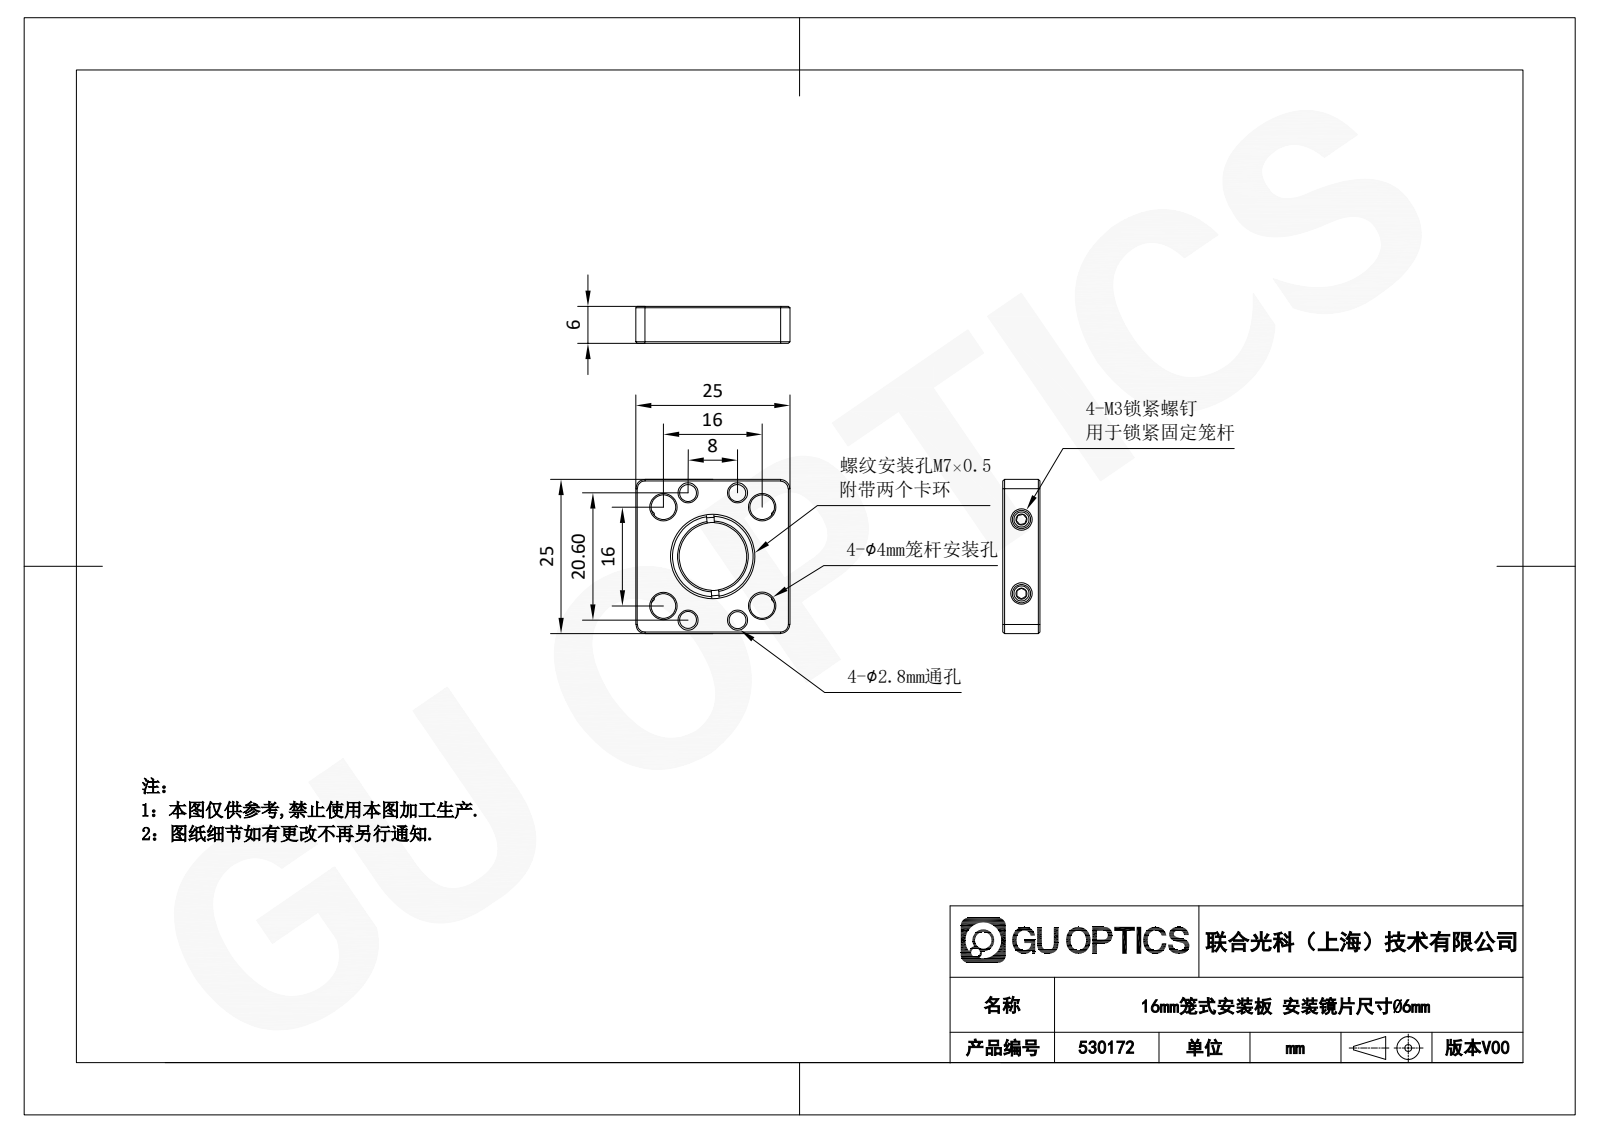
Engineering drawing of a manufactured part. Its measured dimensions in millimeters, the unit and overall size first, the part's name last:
Units: millimetres
Overall size (bounding box): 25 × 25 × 6
Round holes (diameter × count): ⌀2.8 ×4, ⌀4 ×4, ⌀2.5 ×2, ⌀4.5 ×1, ⌀6.5 ×1
Round bosses / shafts (diameter × count): ⌀3 ×2, ⌀7 ×1
Partial cylindrical surfaces — rounded edges, fillets, slot ends (radius × count): R1.5 ×4
Main face-to-face distances: 6, 25, 2, 21.56, 4, 3, 22, 1.5, 1, 24
Hole centre spacings: 4.61, 11.05, 11.31, 12.22, 16, 18.73, 21.88, 8
Volume: 3 137 mm³ · Surface area: 2 655 mm²
Bodies: 7 solids, 283 faces (134 planar, 25 cylindrical, 124 other)
Part name (STEP PRODUCT): 530172
STEP written by: SolidWorks 2020 (CONFIG_CONTROL_DESIGN)
